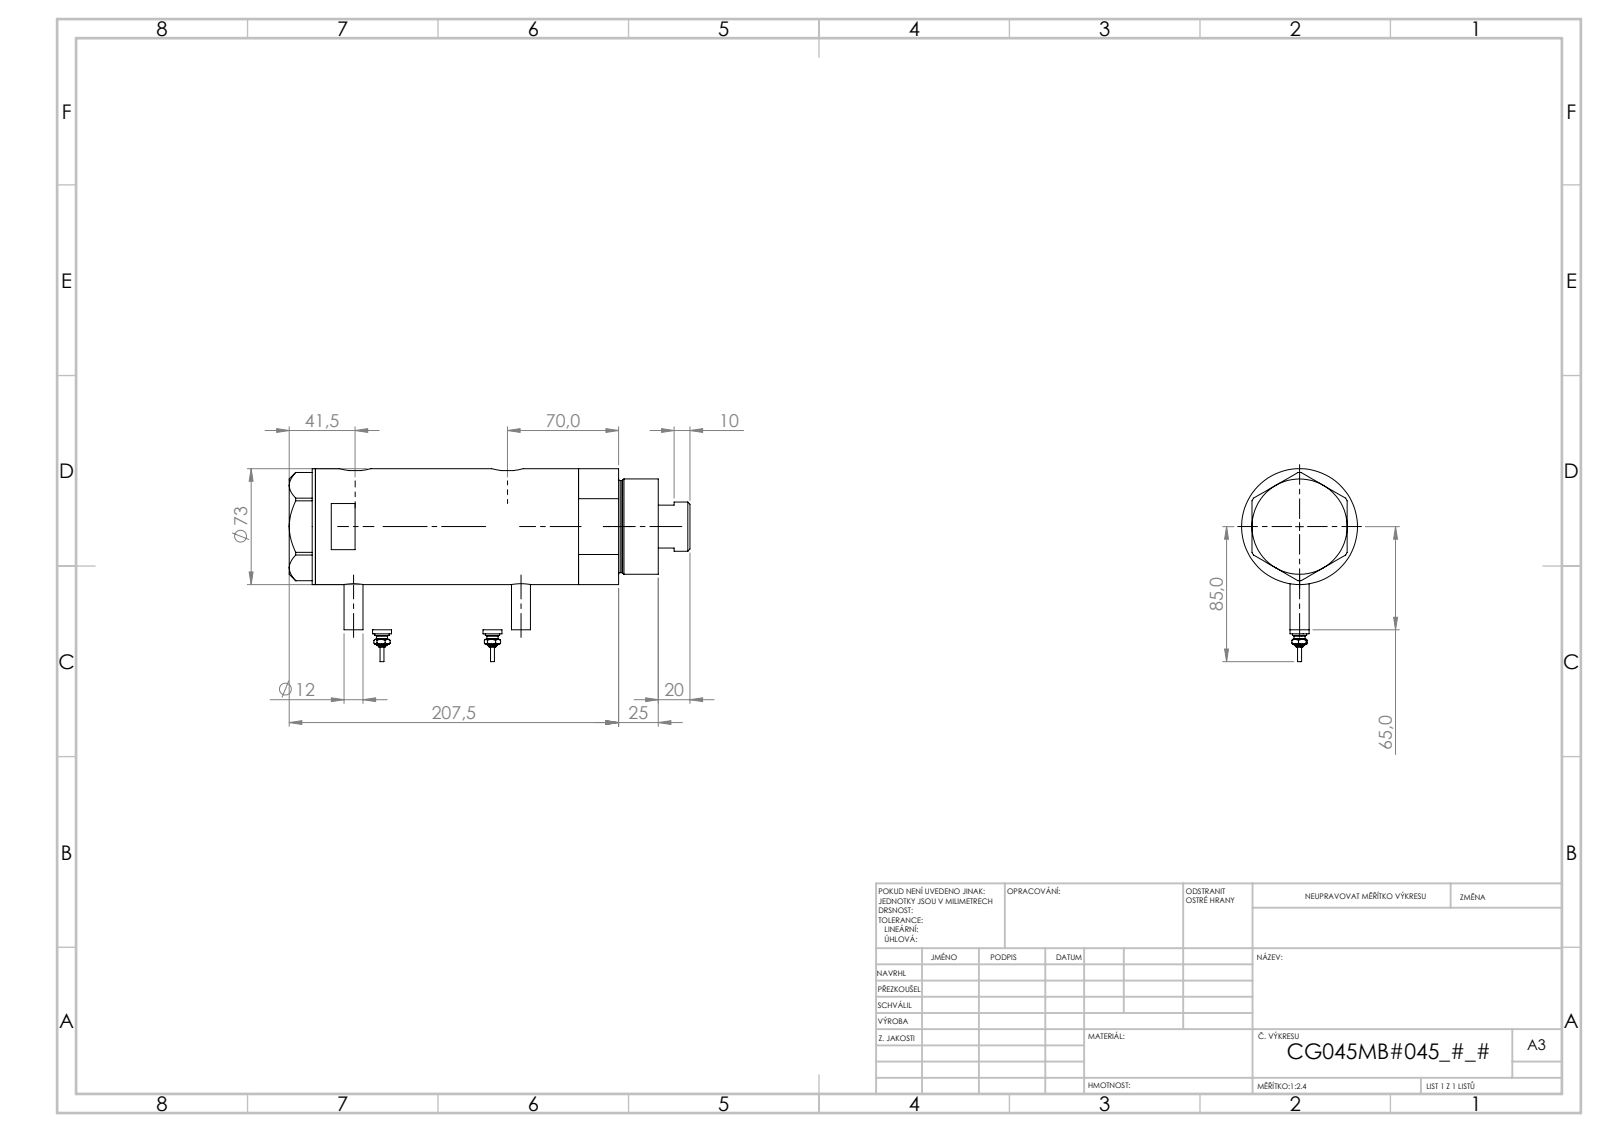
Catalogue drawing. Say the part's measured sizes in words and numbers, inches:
The part is named "V270CG_MIDDLE; V270CG_BACK; V270CG_VC; V270CG_FRONT (+1 more)". Its 3-D file was written by "SolidWorks 2019 (CONFIG_CONTROL_DESIGN)". It is 6 solids with 231 faces: 78 planar, 79 cylindrical and 74 other. Overall it measures 9.312 by 4.146 by 2.874 inches. Its volume is 50.2 cubic inches and its surface area 221.8 square inches. Round holes: 2 of diameter 0.197, 2 of diameter 0.492, 2 of diameter 0.518, 1 of diameter 0.413, 1 of diameter 1.26, 1 of diameter 1.319, 1 of diameter 1.772, 1 of diameter 1.89, 1 of diameter 2.52. Round bosses or shafts: 3 of diameter 0.472, 2 of diameter 0.354, 2 of diameter 0.276, 2 of diameter 0.171, 2 of diameter 0.094, 1 of diameter 2.874, 1 of diameter 2.362, 1 of diameter 2.283. Partial cylindrical surfaces (rounded edges, fillets, slot ends): 2 of radius 0.394. The main face-to-face distances are 4.415, 1.024, 3.391, 0.65, 1.673, 5.065, 7.874, 8.524, 6.851, 3.459. The hole center spacings are 3.805, 0.039, 0.039, 0.335, 0.335, 3.431, 3.47, 3.47.
